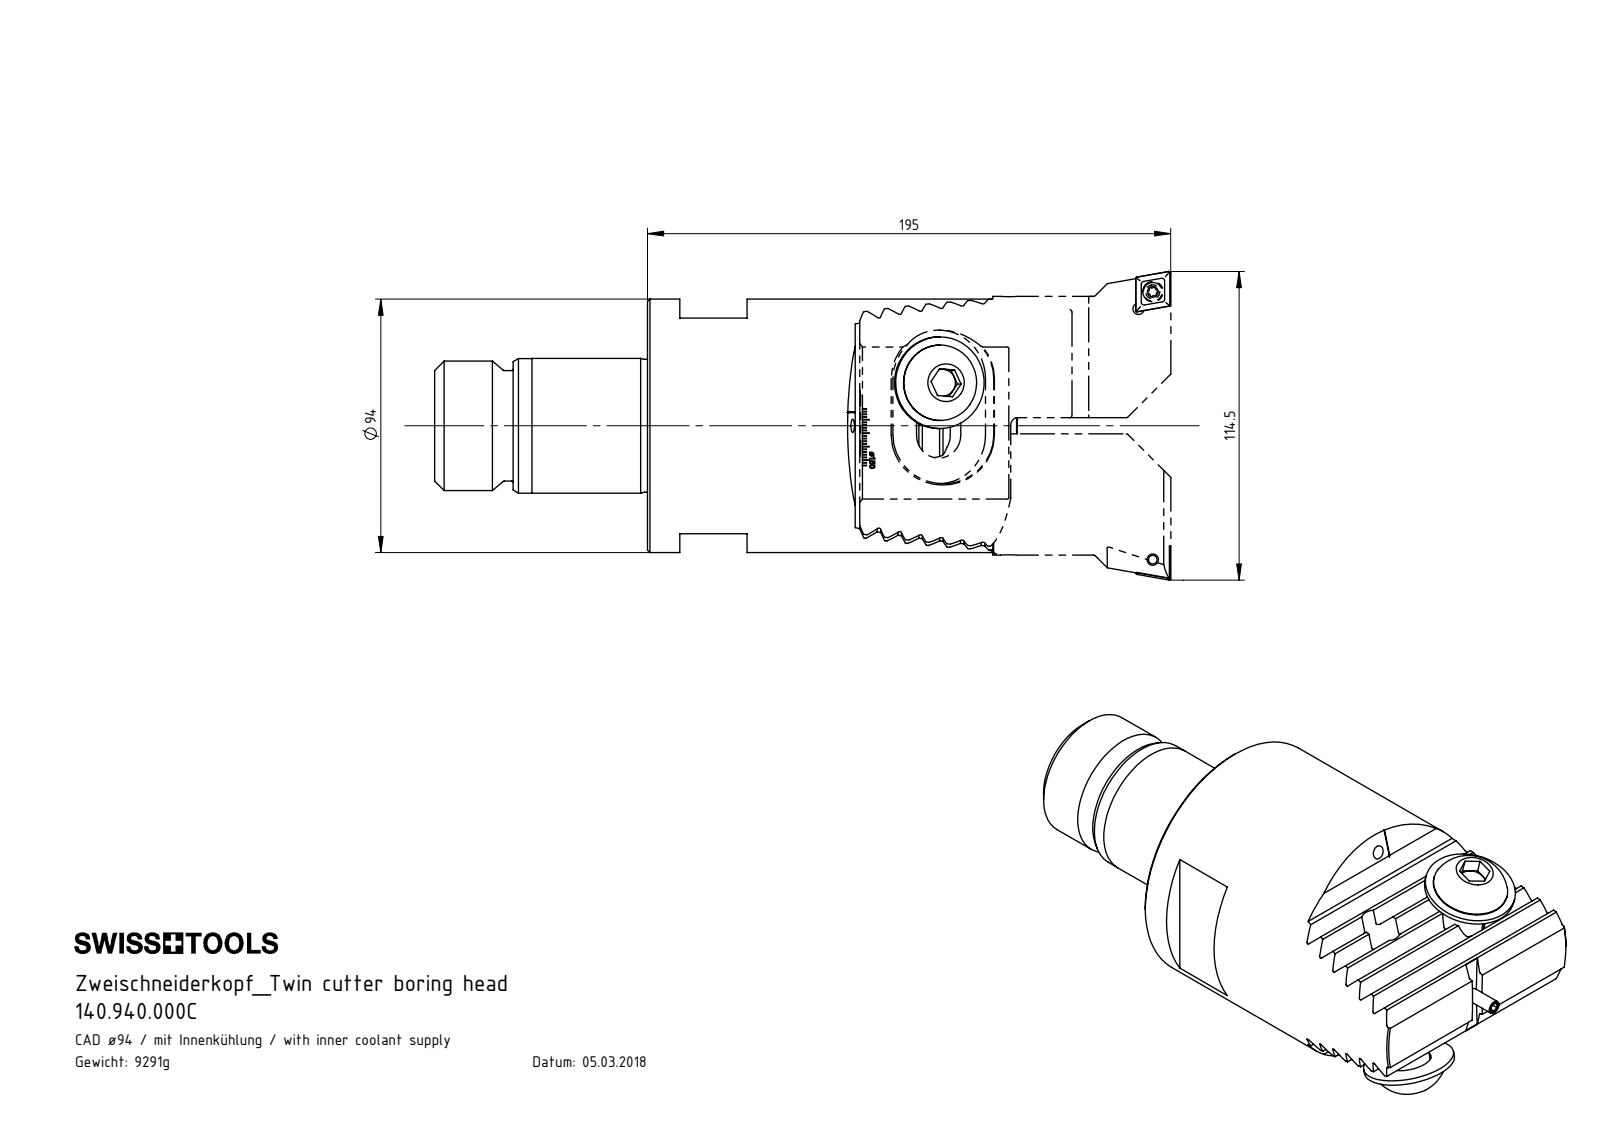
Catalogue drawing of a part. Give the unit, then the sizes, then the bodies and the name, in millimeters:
Units: millimetres
Overall size (bounding box): 216.2 × 94 × 94
Round holes (diameter × count): ⌀5 ×3, ⌀14 ×2, ⌀17 ×2, ⌀17.5 ×2, ⌀3 ×1, ⌀3.3 ×1, ⌀8.5 ×1
Round bosses / shafts (diameter × count): ⌀34 ×2, ⌀28 ×2, ⌀16 ×2, ⌀94 ×1, ⌀50 ×1, ⌀49.95 ×1, ⌀49.3 ×1, ⌀48 ×1
Partial cylindrical surfaces — rounded edges, fillets, slot ends (radius × count): R0.58 ×14, R220 ×2
Main face-to-face distances: 6.93, 13.86, 27.71, 20.78, 13.85, 34.64, 20.79, 128.2, 6.92, 1.8
Volume: 841 848 mm³ · Surface area: 84 575 mm²
Bodies: 6 solids, 306 faces (141 planar, 93 cylindrical, 72 other)
Part name (STEP PRODUCT): Z94-ER1.002.035_A; Z94-ER1.003.035_A_gespannt; Z94-ER1.001.035; Z42-ER2.001.019_A (+2 more)
STEP written by: SolidWorks 2017 (CONFIG_CONTROL_DESIGN)
